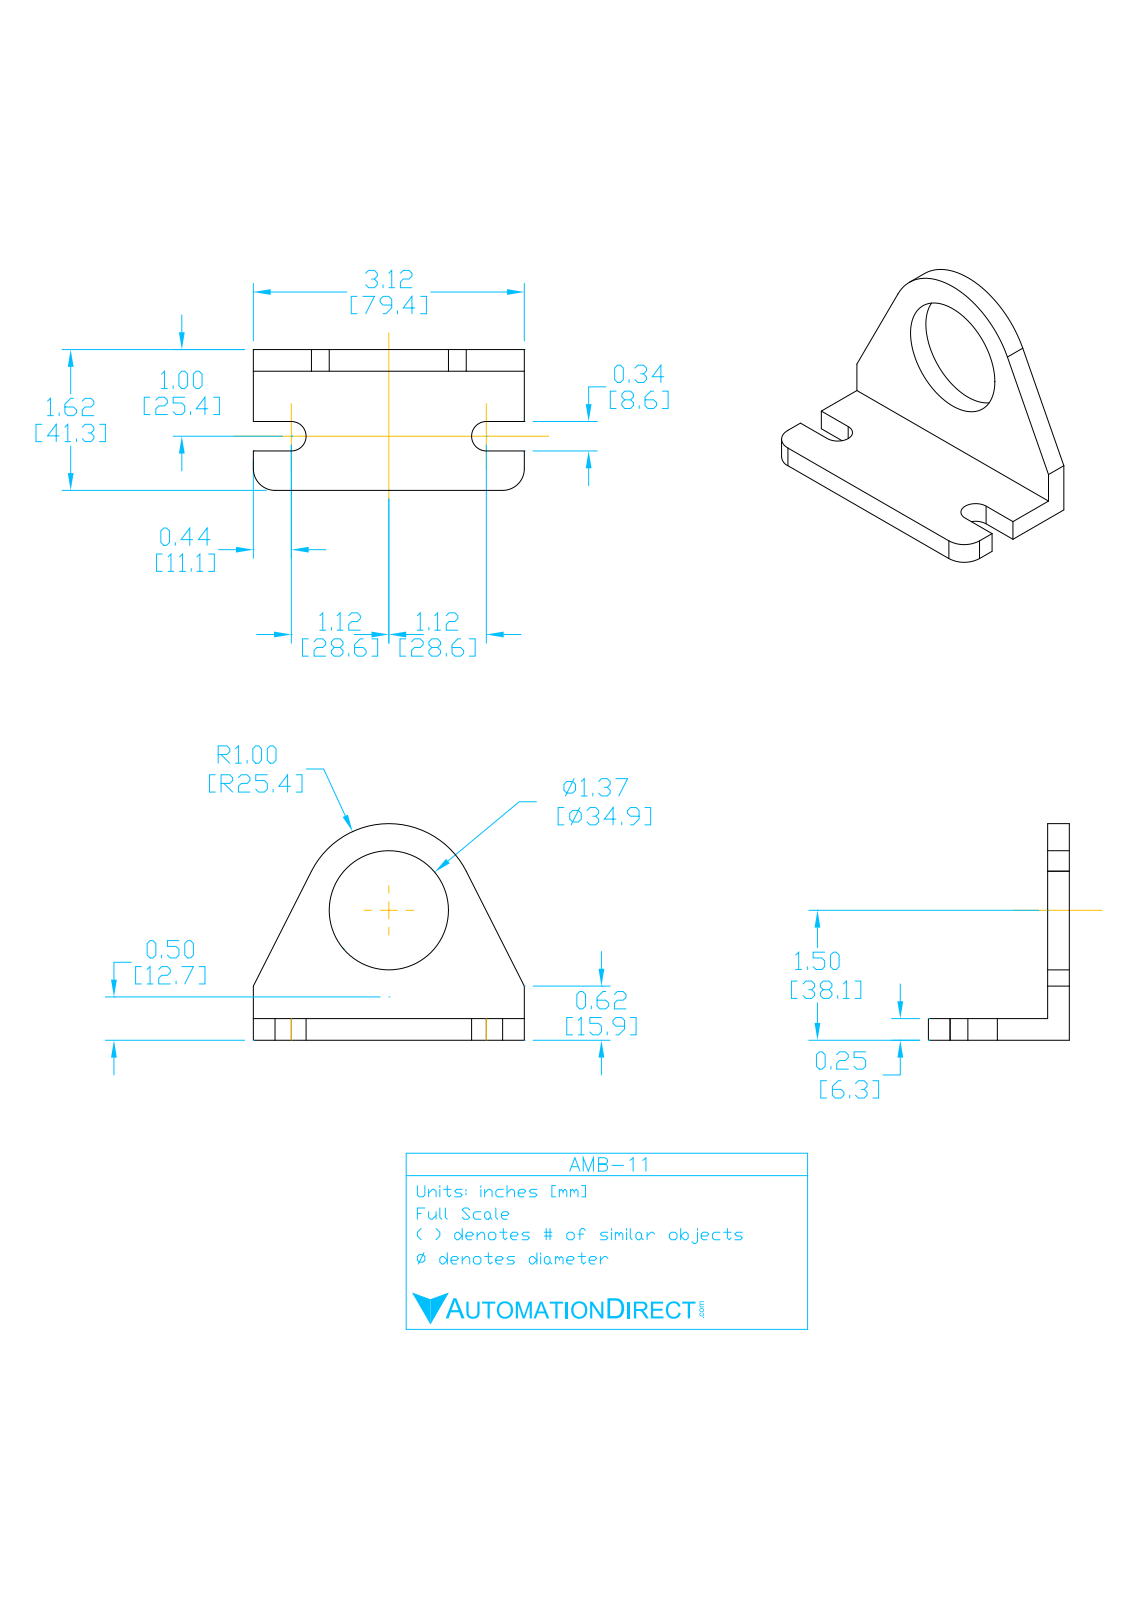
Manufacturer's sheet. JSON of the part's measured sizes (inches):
{"part_name": "AMB-11", "step_written_by": "SolidWorks 2017 (AUTOMOTIVE_DESIGN)", "units": "inches", "bodies": {"solids": 1, "faces": 28, "planar": 19, "cylindrical": 9, "other": 0}, "overall_size": [3.125, 2.5, 1.625], "volume_in3": 2.002, "surface_area_in2": 20.57, "round_holes": [[1.374, 1]], "partial_cylinders_radius": [[0.169, 2], [0.437, 2], [0.06, 1], [0.31, 1], [1, 1]], "face_to_face_distances": [0.25, 1.375, 1.625, 3.125, 0.456, 0.919, 1.169, 0.794, 0.339, 0.581]}
